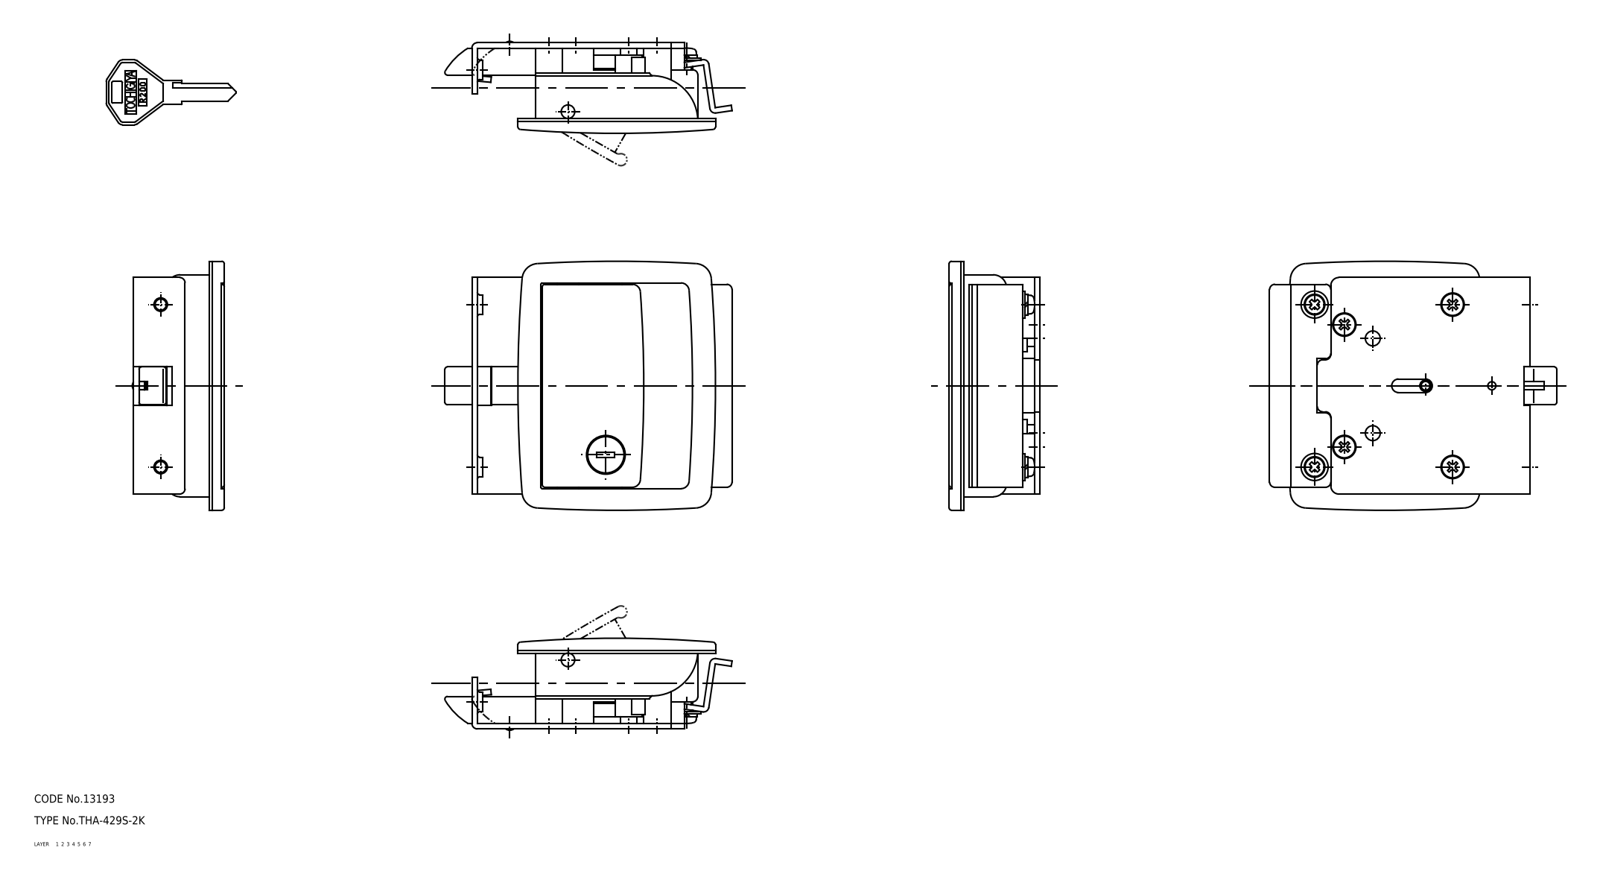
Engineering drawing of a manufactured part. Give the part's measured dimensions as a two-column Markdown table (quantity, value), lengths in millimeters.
| quantity | value |
| --- | --- |
| part name | screw; shaft; packing; lock (+7 more) |
| STEP written by | CADfix (AUTOMOTIVE_DESIGN) |
| units | millimeters |
| bodies | 11 solids, 612 faces (0 planar, 0 cylindrical, 612 other) |
| overall size | 119.75 × 106.28 × 92 |
| volume | 88 676 mm³ |
| surface area | 70 979 mm² |
